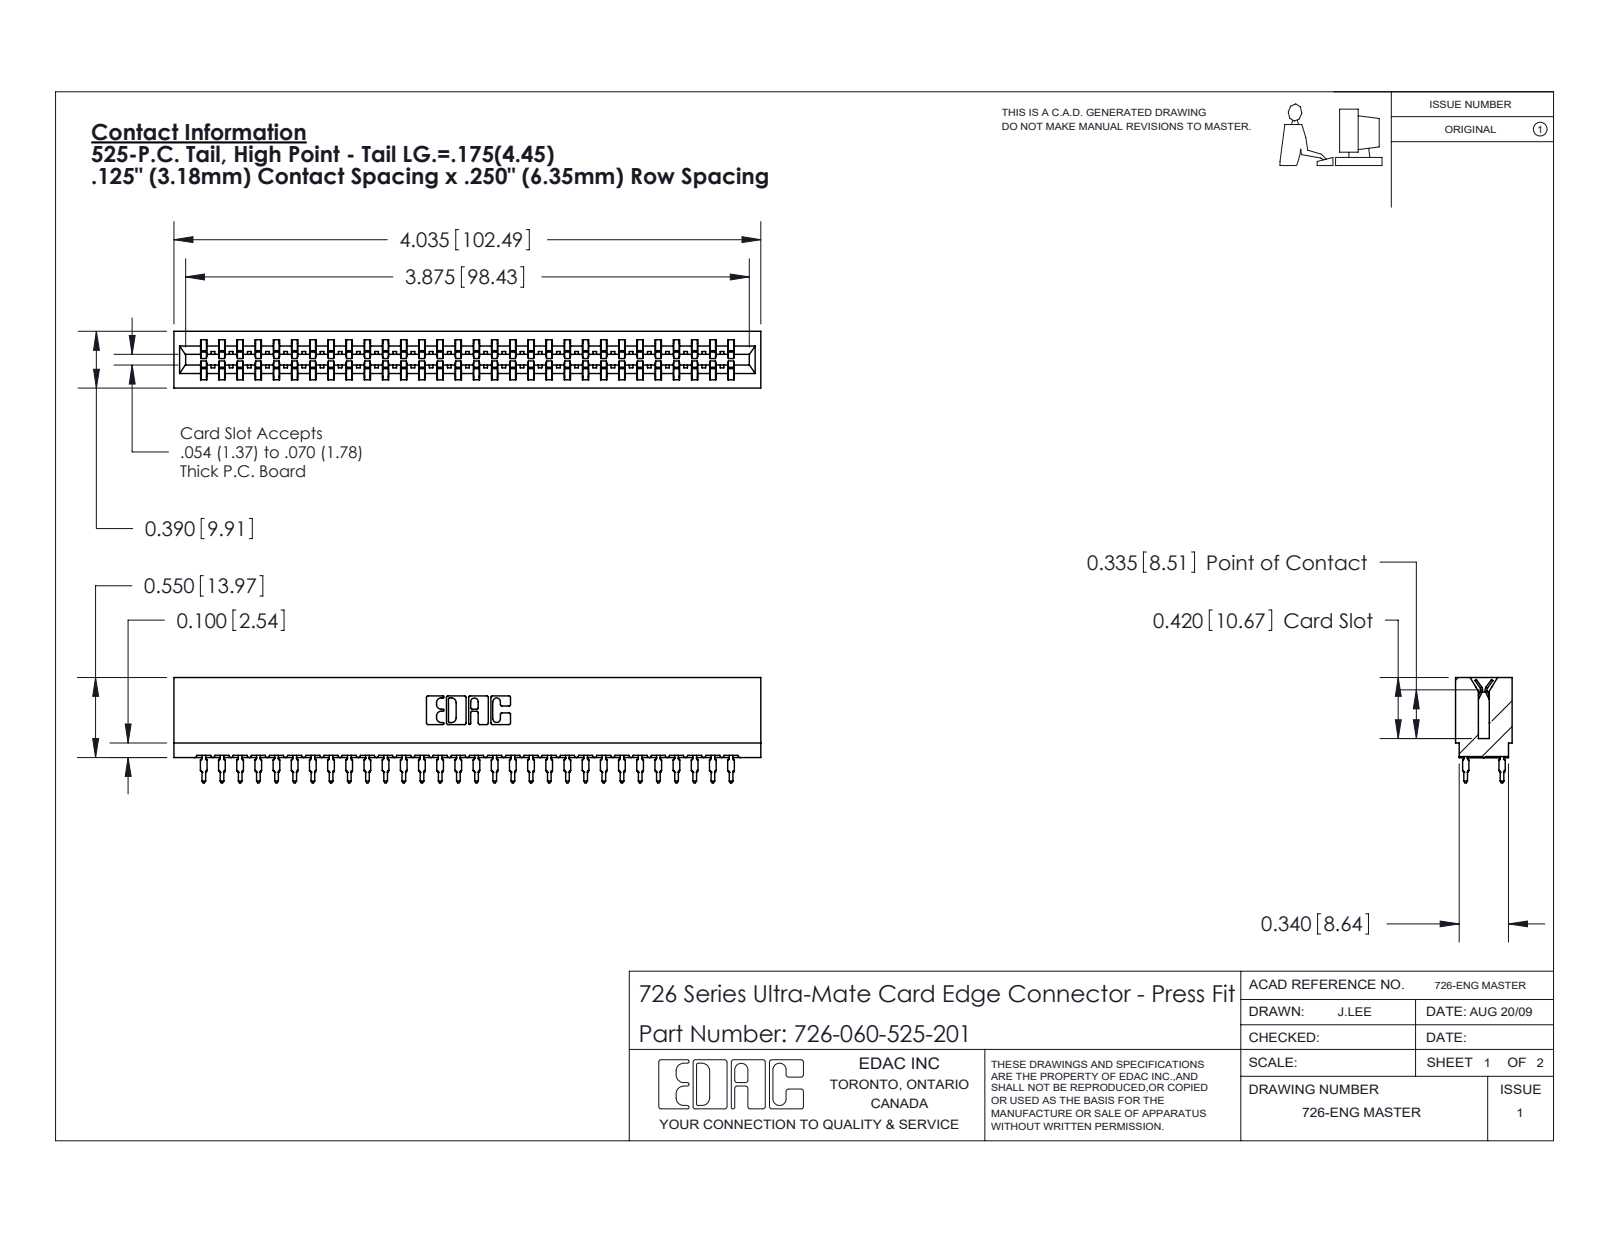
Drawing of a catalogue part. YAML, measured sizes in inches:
part_name: "726-060-525-201; 746-292-001_525; 726 Part_.515 Slot Depth - 01"
step_written_by: "SolidWorks 2020 (CONFIG_CONTROL_DESIGN)"
units: inches
bodies: {solids: 61, faces: 5467, planar: 2815, cylindrical: 1092, other: 1560}
overall_size: [4.035, 0.724, 0.39]
volume: 0.577
surface_area: 23.91
partial_cylinders:
  - {radius: 0.021, count: 120}
  - {radius: 0.015, count: 31}
  - {radius: 0.01, count: 22}
  - {radius: 0.005, count: 8}
  - {radius: 0.011, count: 8}
  - {radius: 0.007, count: 6}
  - {radius: 0.031, count: 6}
  - {radius: 0.026, count: 3}
face_to_face_distances: [0.057, 0.333, 0.39, 0.25, 0.025, 0.307, 0.275, 0.083, 0.5, 0.75]
